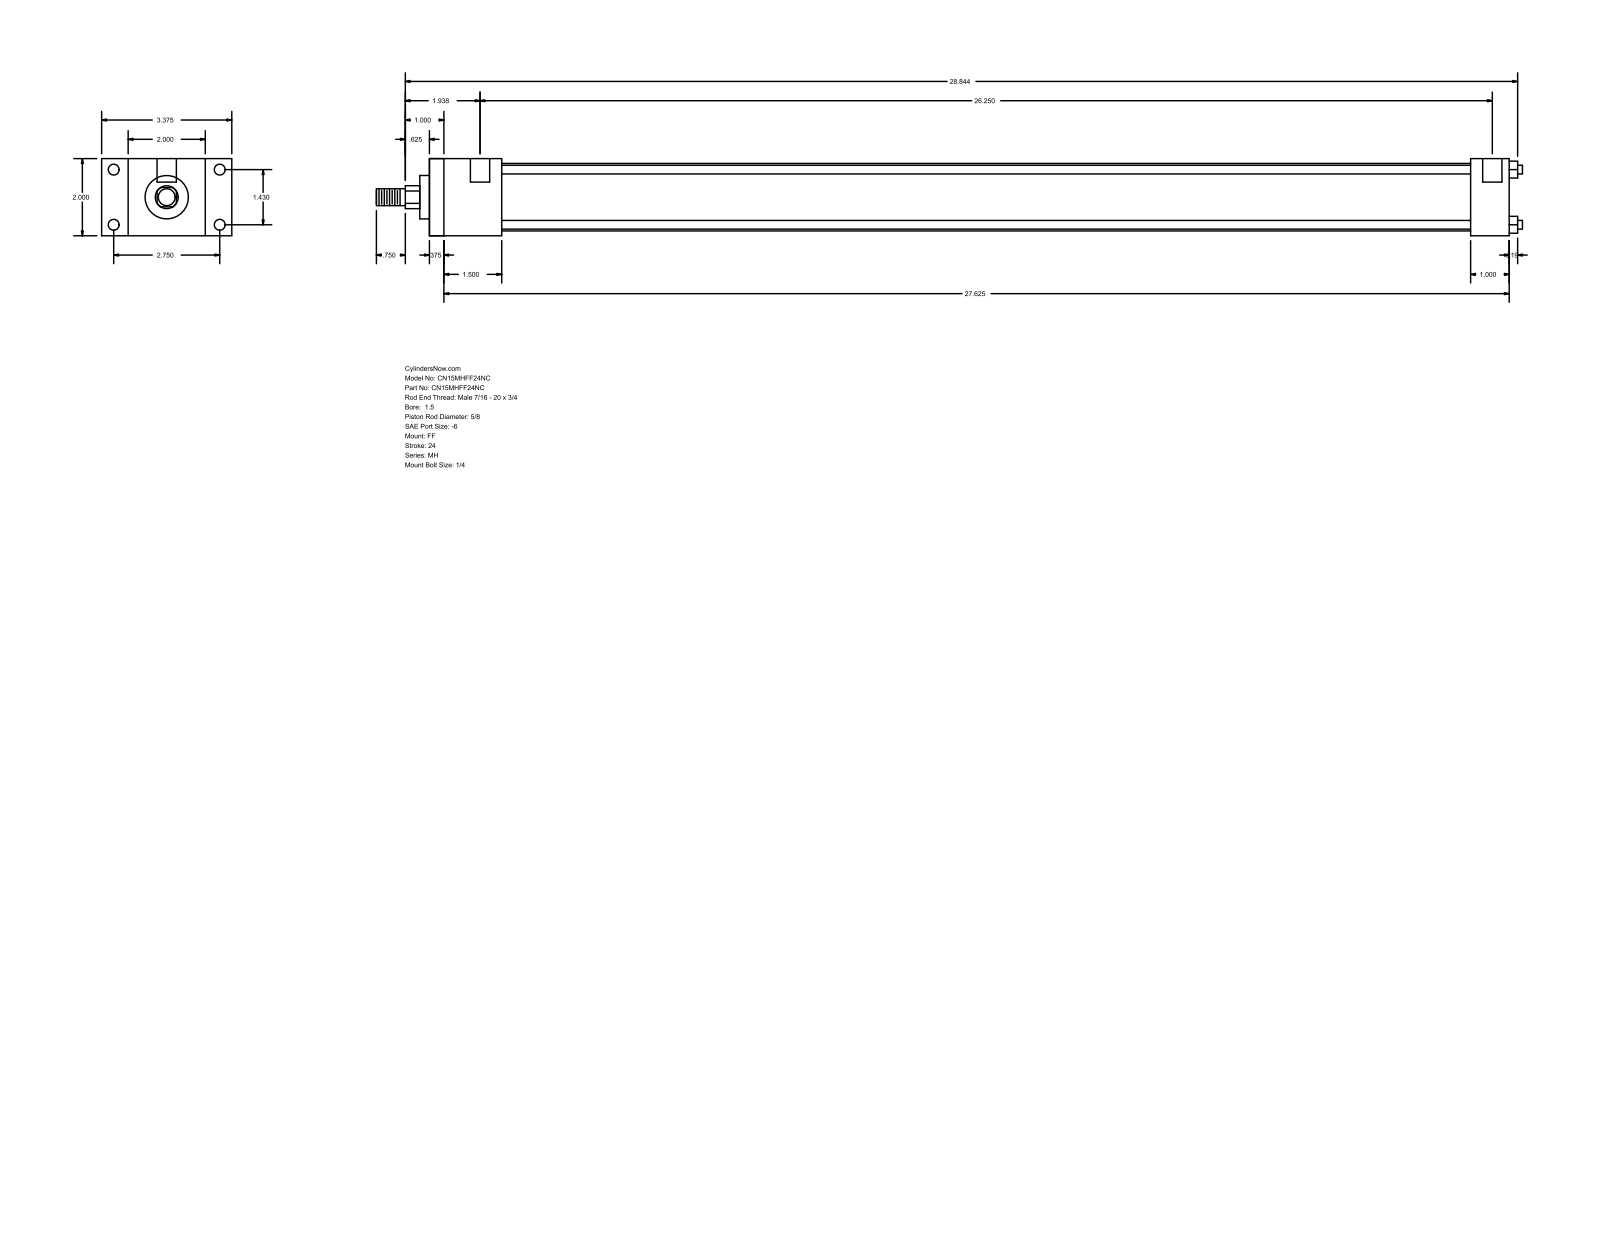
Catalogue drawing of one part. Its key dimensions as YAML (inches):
part_name: "MH_FF__0150_0.625"
step_written_by: "GSSL Pune (CONFIG_CONTROL_DESIGN)"
units: inches
bodies: {solids: 0, faces: 92, planar: 64, cylindrical: 28, other: 0}
overall_size: [29.719, 3.375, 2]
round_holes:
  - {diameter: 0.219, count: 4}
  - {diameter: 0.281, count: 4}
  - {diameter: 0.5, count: 2}
round_bosses_or_shafts:
  - {diameter: 0.225, count: 4}
  - {diameter: 1.75, count: 1}
  - {diameter: 1.125, count: 1}
  - {diameter: 0.625, count: 1}
  - {diameter: 0.437, count: 1}
partial_cylinders:
  - {radius: 0.297, count: 1}
face_to_face_distances: [2, 28, 0.375, 27.625, 0.687, 2.687, 1.875, 1.5, 26.125, 27]
hole_center_spacings: [1.43, 2.75, 3.099, 26.375, 0.125, 26.25]
